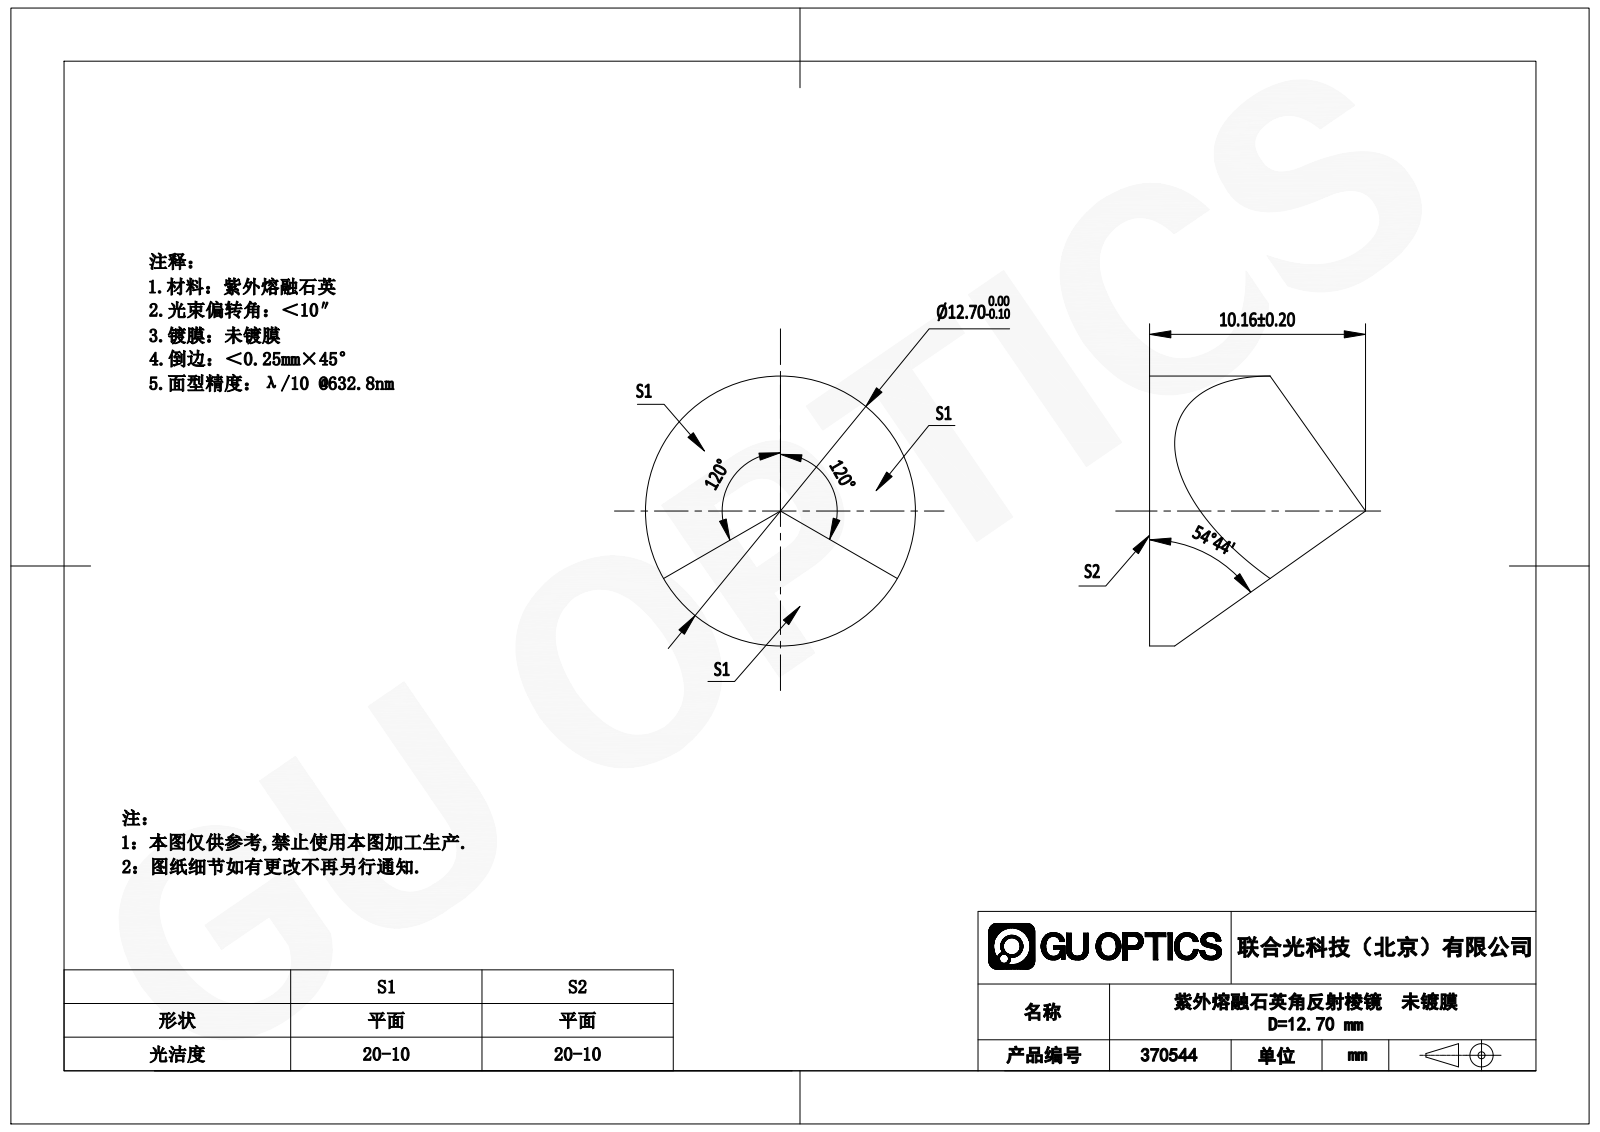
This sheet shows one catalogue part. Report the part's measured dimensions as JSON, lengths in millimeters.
{"part_name": "GP26-012-2", "step_written_by": "SolidWorks 2022 (AUTOMOTIVE_DESIGN)", "units": "millimeters", "bodies": {"solids": 1, "faces": 12, "planar": 8, "cylindrical": 2, "other": 2}, "overall_size": [12.7, 12.7, 10.04], "volume_mm3": 660, "surface_area_mm2": 451, "round_bosses_or_shafts": [[12.7, 1]], "face_to_face_distances": [10.04]}
